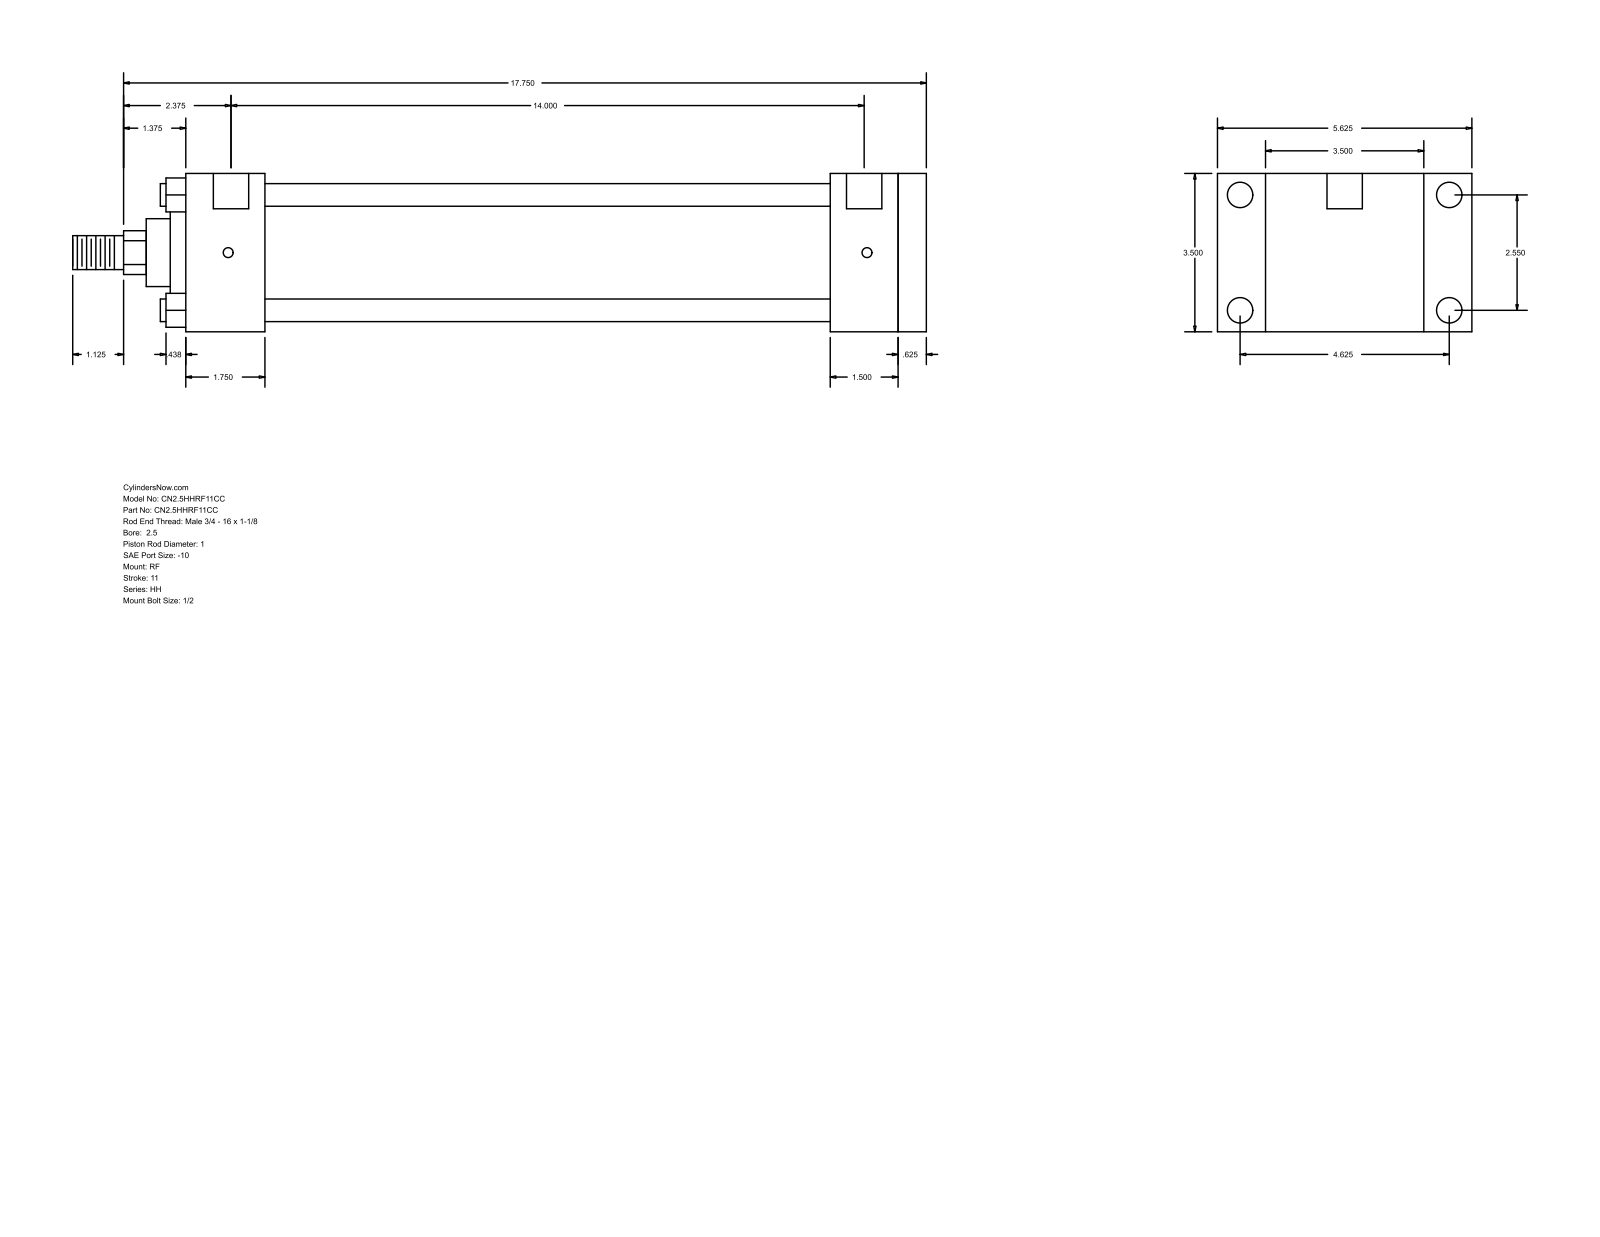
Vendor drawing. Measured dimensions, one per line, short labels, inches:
name: HH_RF__0250_1
written by: GSSL Pune (CONFIG_CONTROL_DESIGN)
unit: in
bodies: 0 solids, 94 faces (65 planar, 29 cylindrical, 0 other)
size: 18.875 × 5.625 × 3.5
holes: 4× ⌀0.219, 4× ⌀0.563, 2× ⌀0.781
bosses: 4× ⌀0.5, 1× ⌀2.875, 1× ⌀2.375, 1× ⌀1.5, 1× ⌀1, 1× ⌀0.75
rounds: 1× R0.484
face distances: 3.5, 0.625, 15.75, 16.375, 1.5, 1.75, 14, 14.625, 14.25, 12.5
hole spacings: 2.55, 4.625, 5.281, 14.125, 0.062, 0.063, 14, 14.062
